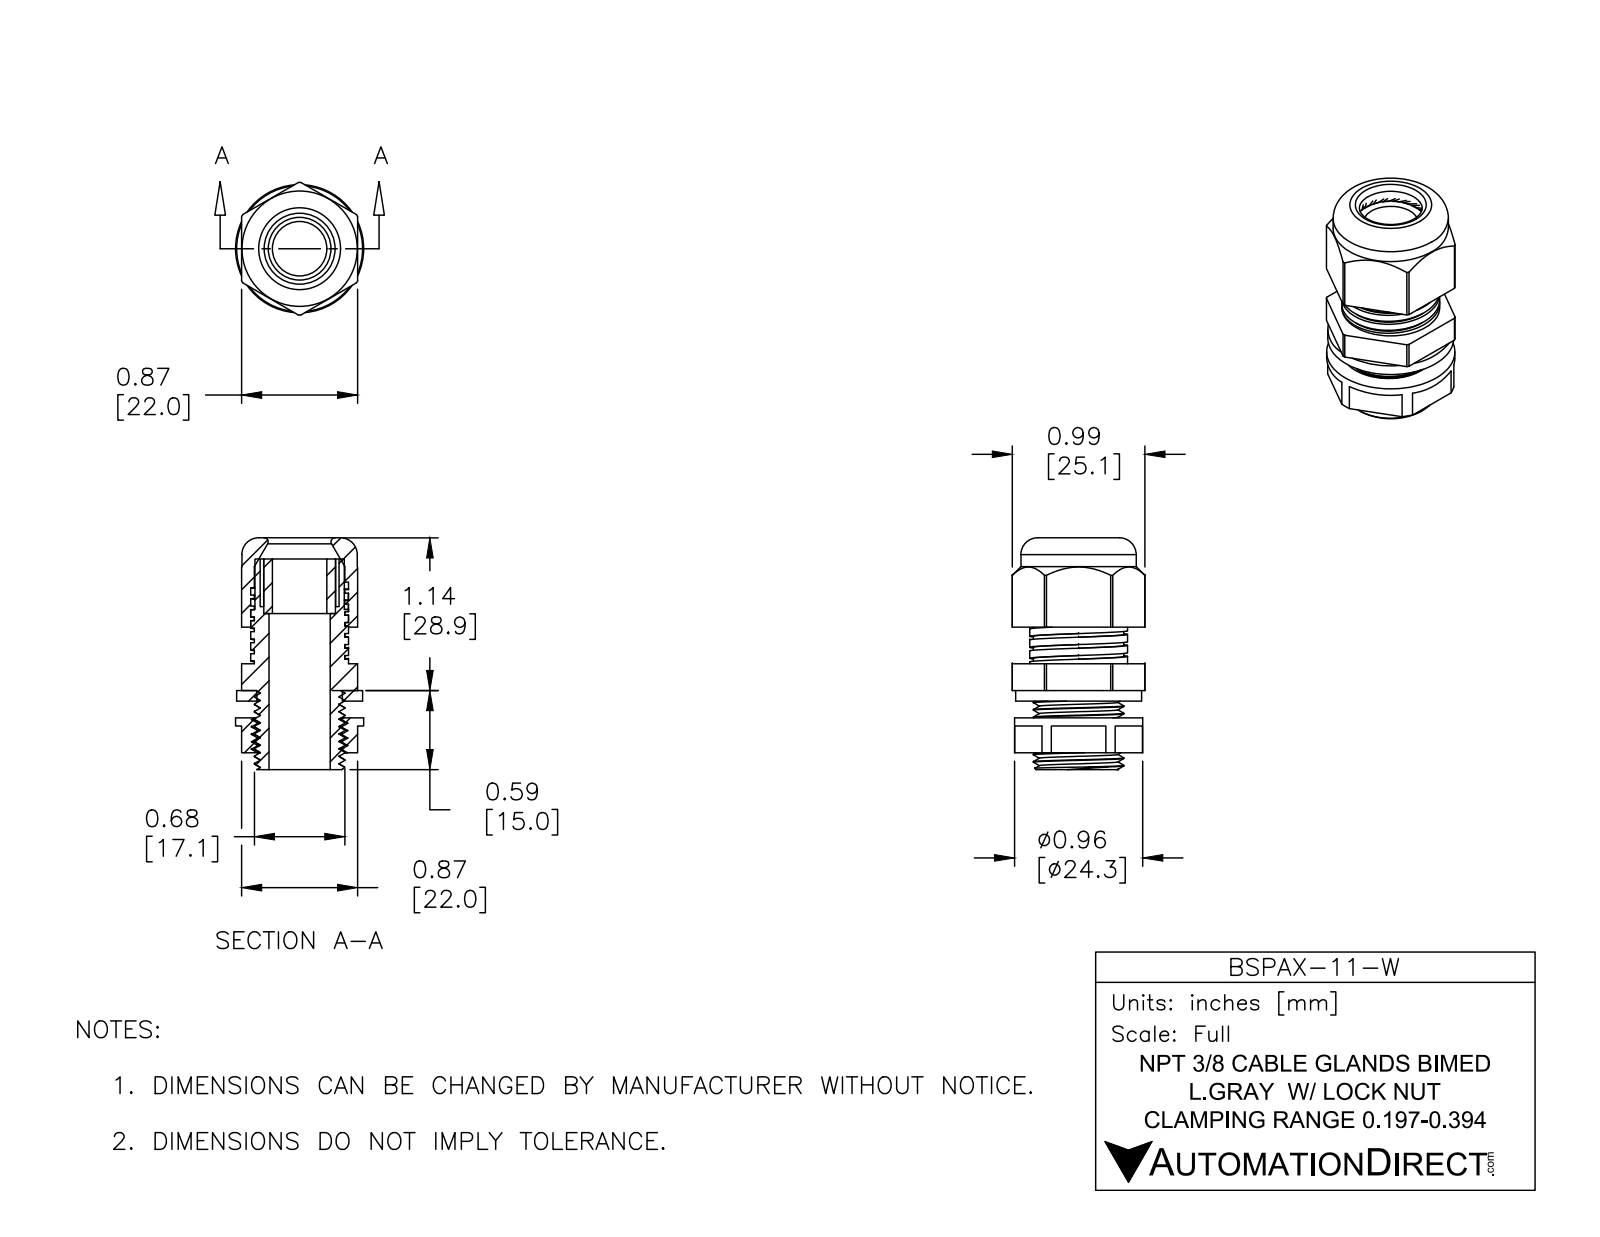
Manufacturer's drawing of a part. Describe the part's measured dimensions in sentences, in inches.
The part is named "BSPAX-11-W". Its 3-D file was written by "SolidWorks 2015 (CONFIG_CONTROL_DESIGN)". It is 5 solids with 236 faces: 127 planar, 84 cylindrical and 25 other. Overall it measures 1.73 by 0.99 by 0.957 inches. Its volume is 0.64 cubic inches and its surface area 18.93 square inches. Round holes: 1 of diameter 0.406, 1 of diameter 0.457, 1 of diameter 0.534, 1 of diameter 0.631, 1 of diameter 0.638, 1 of diameter 0.676. Round bosses or shafts: 1 of diameter 0.957, 1 of diameter 0.94, 1 of diameter 0.86, 1 of diameter 0.73, 1 of diameter 0.675, 1 of diameter 0.667. Partial cylindrical surfaces (rounded edges, fillets, slot ends): 1 of radius 0.495. The main face-to-face distances are 0.866, 0.02, 0.442, 0.462, 0.079, 0.464, 0.125, 0.204, 0.664, 0.2.
